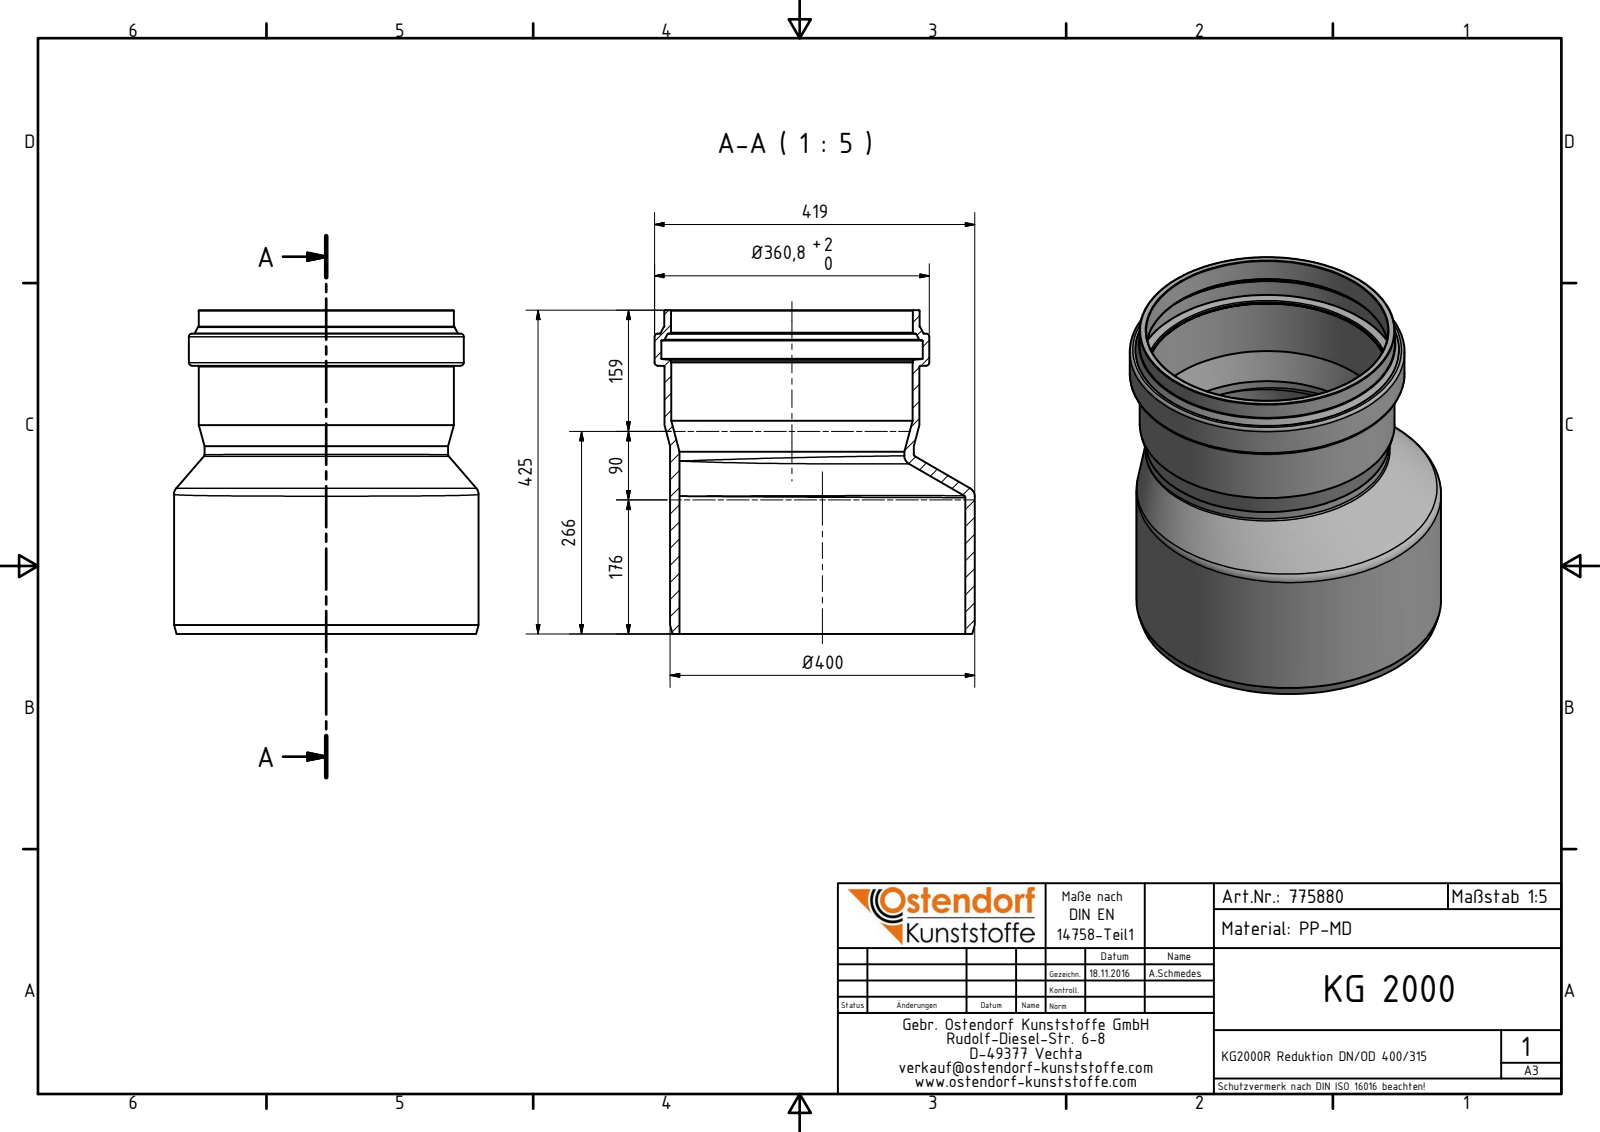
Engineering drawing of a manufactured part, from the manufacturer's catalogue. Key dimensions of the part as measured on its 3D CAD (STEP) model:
Part name (STEP PRODUCT): 775880 KG2000R Reduktion DN_OD 400_315
STEP written by: Autodesk Inventor 2016 (AUTOMOTIVE_DESIGN)
Units: millimetres
Bodies: 1 solid, 44 faces (5 planar, 11 cylindrical, 28 other)
Overall size (bounding box): 425 × 420.45 × 400
Volume: 5 713 000 mm³ · Surface area: 1 052 000 mm²
Round holes (diameter × count): ⌀295.3 ×1, ⌀317.1 ×1, ⌀317.5 ×1, ⌀343.2 ×1, ⌀375.4 ×1
Round bosses / shafts (diameter × count): ⌀400 ×1, ⌀360.8 ×1, ⌀335.1 ×1, ⌀334.7 ×1, ⌀319.9 ×1
Main face-to-face distances: 352.1, 425, 72.9, 394.1, 42, 30.9, 356.33, 4.23, 37.77, 68.67
Hole centre spacings: 40.05
